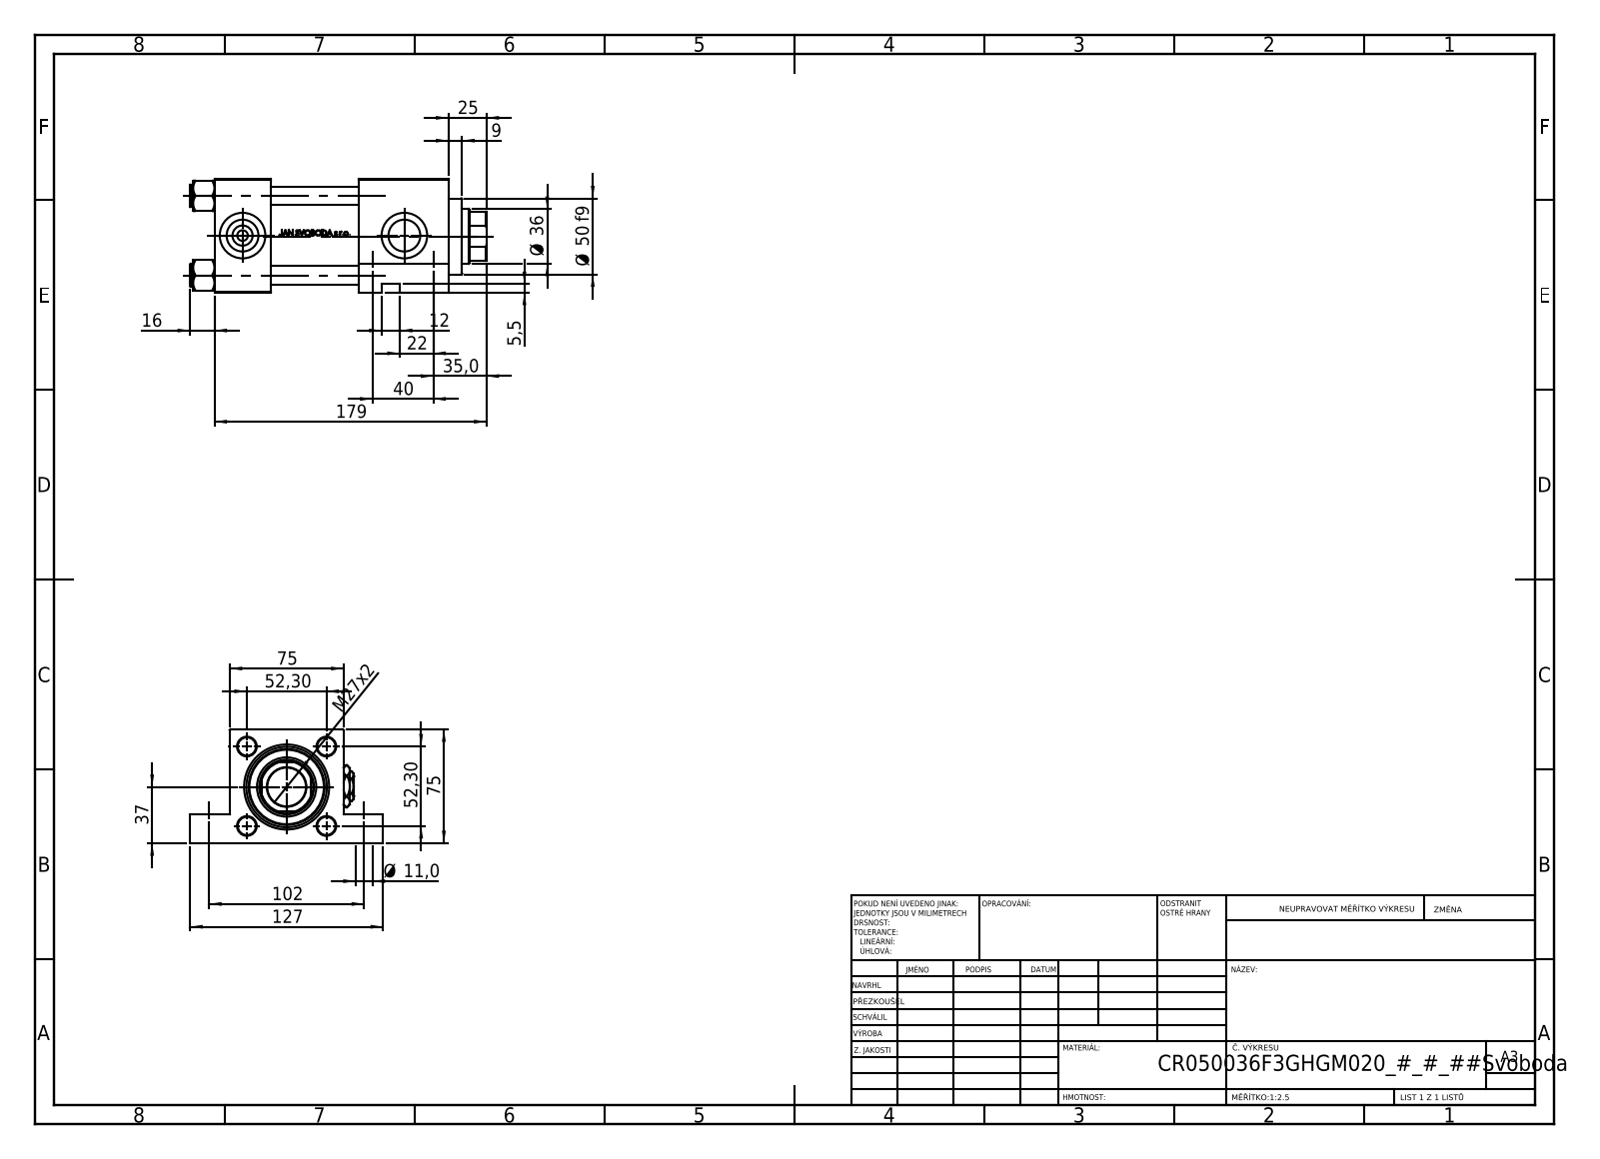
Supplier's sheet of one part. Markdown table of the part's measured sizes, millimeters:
| quantity | value |
| --- | --- |
| part name | V215CR_F_Body; NUT_M5_F; V215CR_VCP_F; V215_VC_A (+2 more) |
| STEP written by | SolidWorks 2019 (CONFIG_CONTROL_DESIGN) |
| units | millimeters |
| bodies | 13 solids, 1199 faces (483 planar, 134 cylindrical, 582 other) |
| overall size | 195 × 127 × 75 |
| volume | 731 211 mm³ |
| surface area | 168 811 mm² |
| round holes (diameter × count) | 12 × 4, 20.96 × 3, 30 × 3, 7 × 2, 11 × 2, 11 × 2, 17 × 1, 25.5 × 1, 36 × 1, 39 × 1, 41 × 1, 53 × 1 |
| round bosses / shafts (diameter × count) | 15 × 4, 56 × 1, 50 × 1 |
| partial cylindrical surfaces (radius × count) | 17.5 × 1 |
| main face-to-face distances | 75, 37, 58, 95, 59, 154, 117, 19, 56, 74.8 |
| hole center spacings | 52.3, 36.63, 37.34, 40, 73.96, 102, 109.56, 13 |
